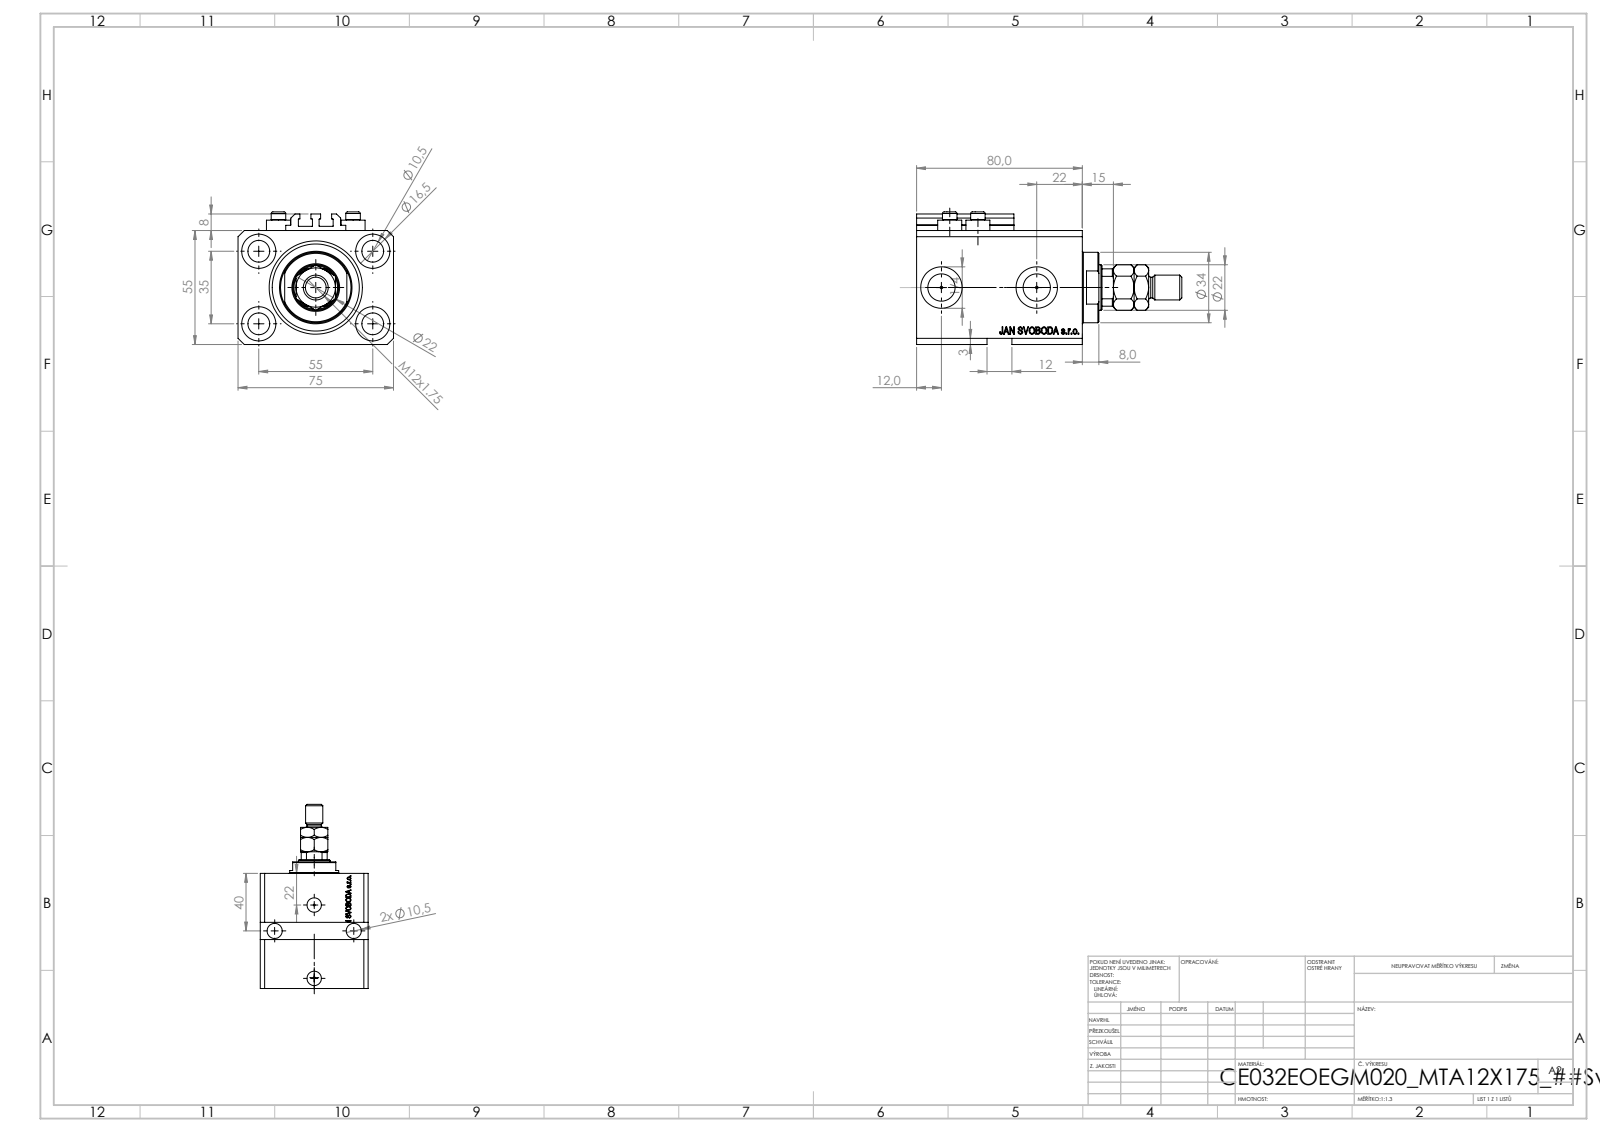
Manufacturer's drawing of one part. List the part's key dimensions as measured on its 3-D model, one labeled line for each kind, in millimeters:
Part name (STEP PRODUCT): ALLEN BOLT V250CE; MTA; V250CE_C_VCP; V250CE_E_Body (+1 more)
STEP written by: SolidWorks 2019 (CONFIG_CONTROL_DESIGN)
Units: millimetres
Bodies: 9 solids, 1113 faces (529 planar, 130 cylindrical, 454 other)
Overall size (bounding box): 128 × 75 × 64
Volume: 290 869 mm³ · Surface area: 76 781 mm²
Round holes (diameter × count): ⌀10.5 ×7, ⌀1.25 ×4, ⌀4 ×4, ⌀16.5 ×4, ⌀10 ×2, ⌀13.16 ×2, ⌀20 ×2, ⌀22 ×1, ⌀32 ×1, ⌀45 ×1
Round bosses / shafts (diameter × count): ⌀11.6 ×4, ⌀7 ×4, ⌀34 ×1, ⌀12 ×1, ⌀10 ×1
Partial cylindrical surfaces — rounded edges, fillets, slot ends (radius × count): R0.2 ×10, R10.5 ×1
Main face-to-face distances: 55, 75, 15, 65, 80, 3, 55.1, 9.9, 70.1, 54
Hole centre spacings: 32.6, 55, 13.6, 14.09, 19.89, 20.12, 25.81, 28.48
